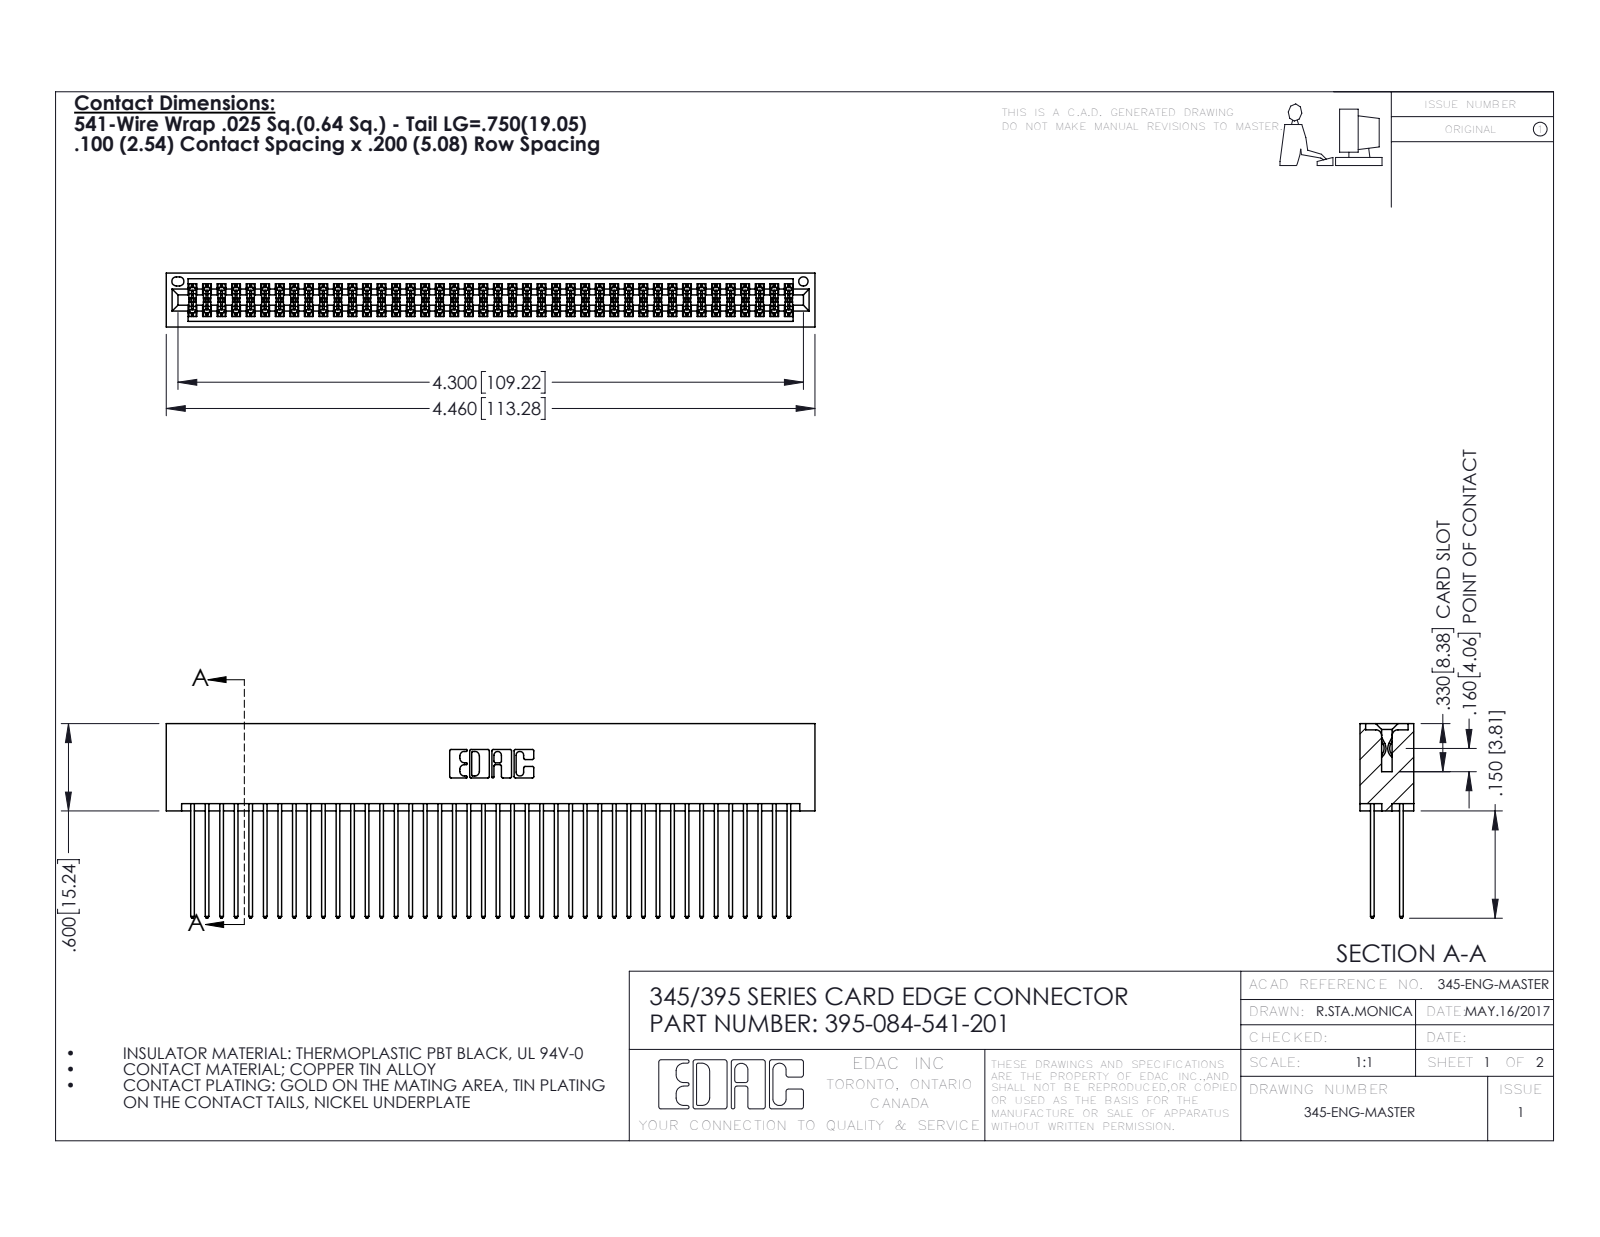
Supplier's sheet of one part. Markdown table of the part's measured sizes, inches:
| quantity | value |
| --- | --- |
| part name | 345 Part_No Mounting Lugs; 395-084-541-201; 345-292-001_345-293-141 |
| STEP written by | SolidWorks 2016 (CONFIG_CONTROL_DESIGN) |
| units | inches |
| bodies | 85 solids, 4318 faces (2848 planar, 1470 cylindrical, 0 other) |
| overall size | 4.46 × 1.337 × 0.37 |
| volume | 0.739 in³ |
| surface area | 31.71 in² |
| round holes (diameter × count) | 0.064 × 1 |
| partial cylindrical surfaces (radius × count) | 0.006 × 126, 0.01 × 84, 0.01 × 22, 0.007 × 6, 0.031 × 6, 0.026 × 3, 0.014 × 2, 0.019 × 2 |
| main face-to-face distances | 0.298, 0.072, 0.2, 0.098, 0.272, 0.025, 0.225, 0.37, 0.175, 0.149 |
